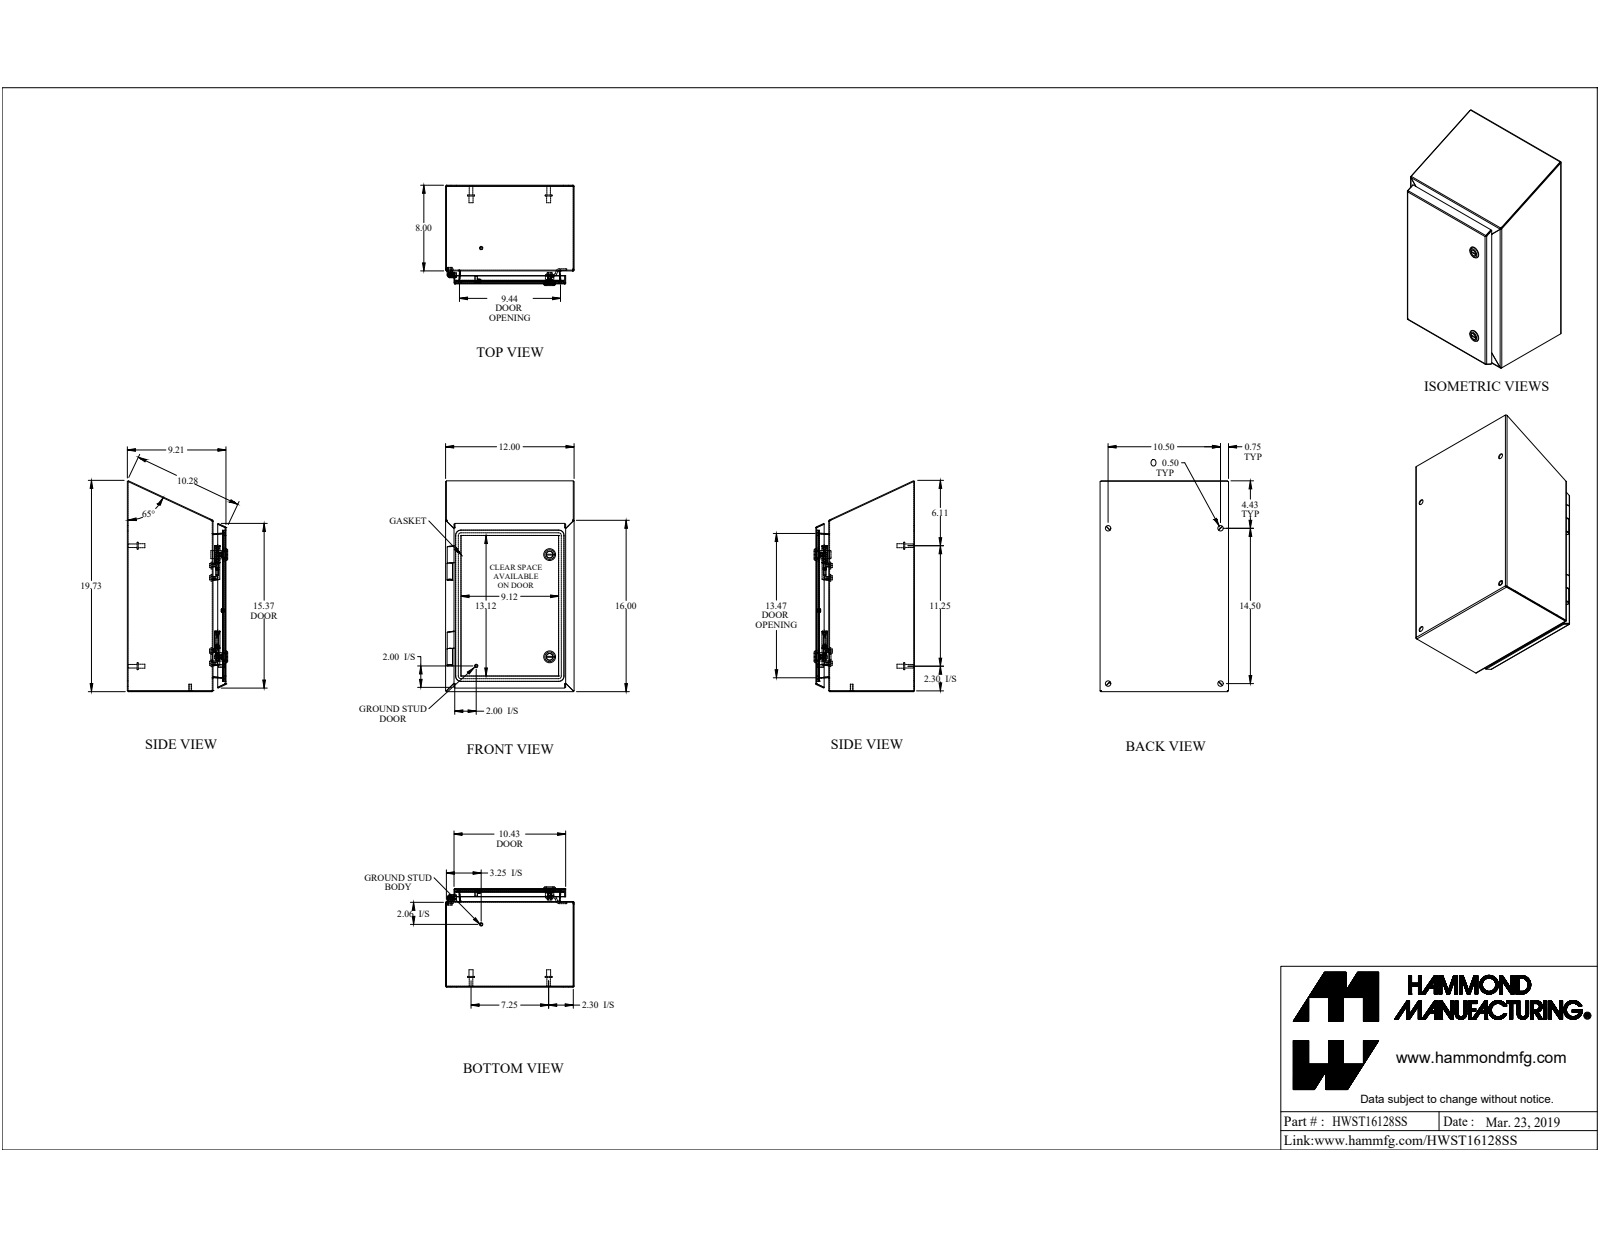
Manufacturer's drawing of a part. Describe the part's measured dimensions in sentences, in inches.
The part is named "HWST16128SS". Its 3-D file was written by "SolidWorks 2019 (AUTOMOTIVE_DESIGN)". It is 43 solids with 1051 faces: 649 planar, 288 cylindrical and 114 other. Overall it measures 19.684 by 12 by 9.37 inches. Its volume is 87.39 cubic inches and its surface area 2 327 square inches. Round holes: 8 of diameter 0.194, 4 of diameter 0.24, 4 of diameter 0.275, 2 of diameter 0.13, 2 of diameter 0.197, 2 of diameter 0.387, 2 of diameter 0.5, 2 of diameter 0.63, 2 of diameter 0.768, 1 of diameter 0.24, 1 of diameter 3.5. Round bosses or shafts: 8 of diameter 0.226, 4 of diameter 0.65, 4 of diameter 0.625, 4 of diameter 0.375, 4 of diameter 0.332, 4 of diameter 0.25, 3 of diameter 0.236, 2 of diameter 1.1. Partial cylindrical surfaces (rounded edges, fillets, slot ends): 24 of radius 0.25, 16 of radius 0.039, 16 of radius 0.108, 12 of radius 0.012, 12 of radius 0.036, 12 of radius 0.125, 9 of radius 0.108, 7 of radius 0.036. The main face-to-face distances are 0.072, 11.928, 9.066, 9.138, 0.072, 9.138, 9.21, 11.856, 12, 7.928. The hole center spacings are 1.142, 7.979, 6.837, 7.98, 9.12, 1.141, 1.143, 3.226.
